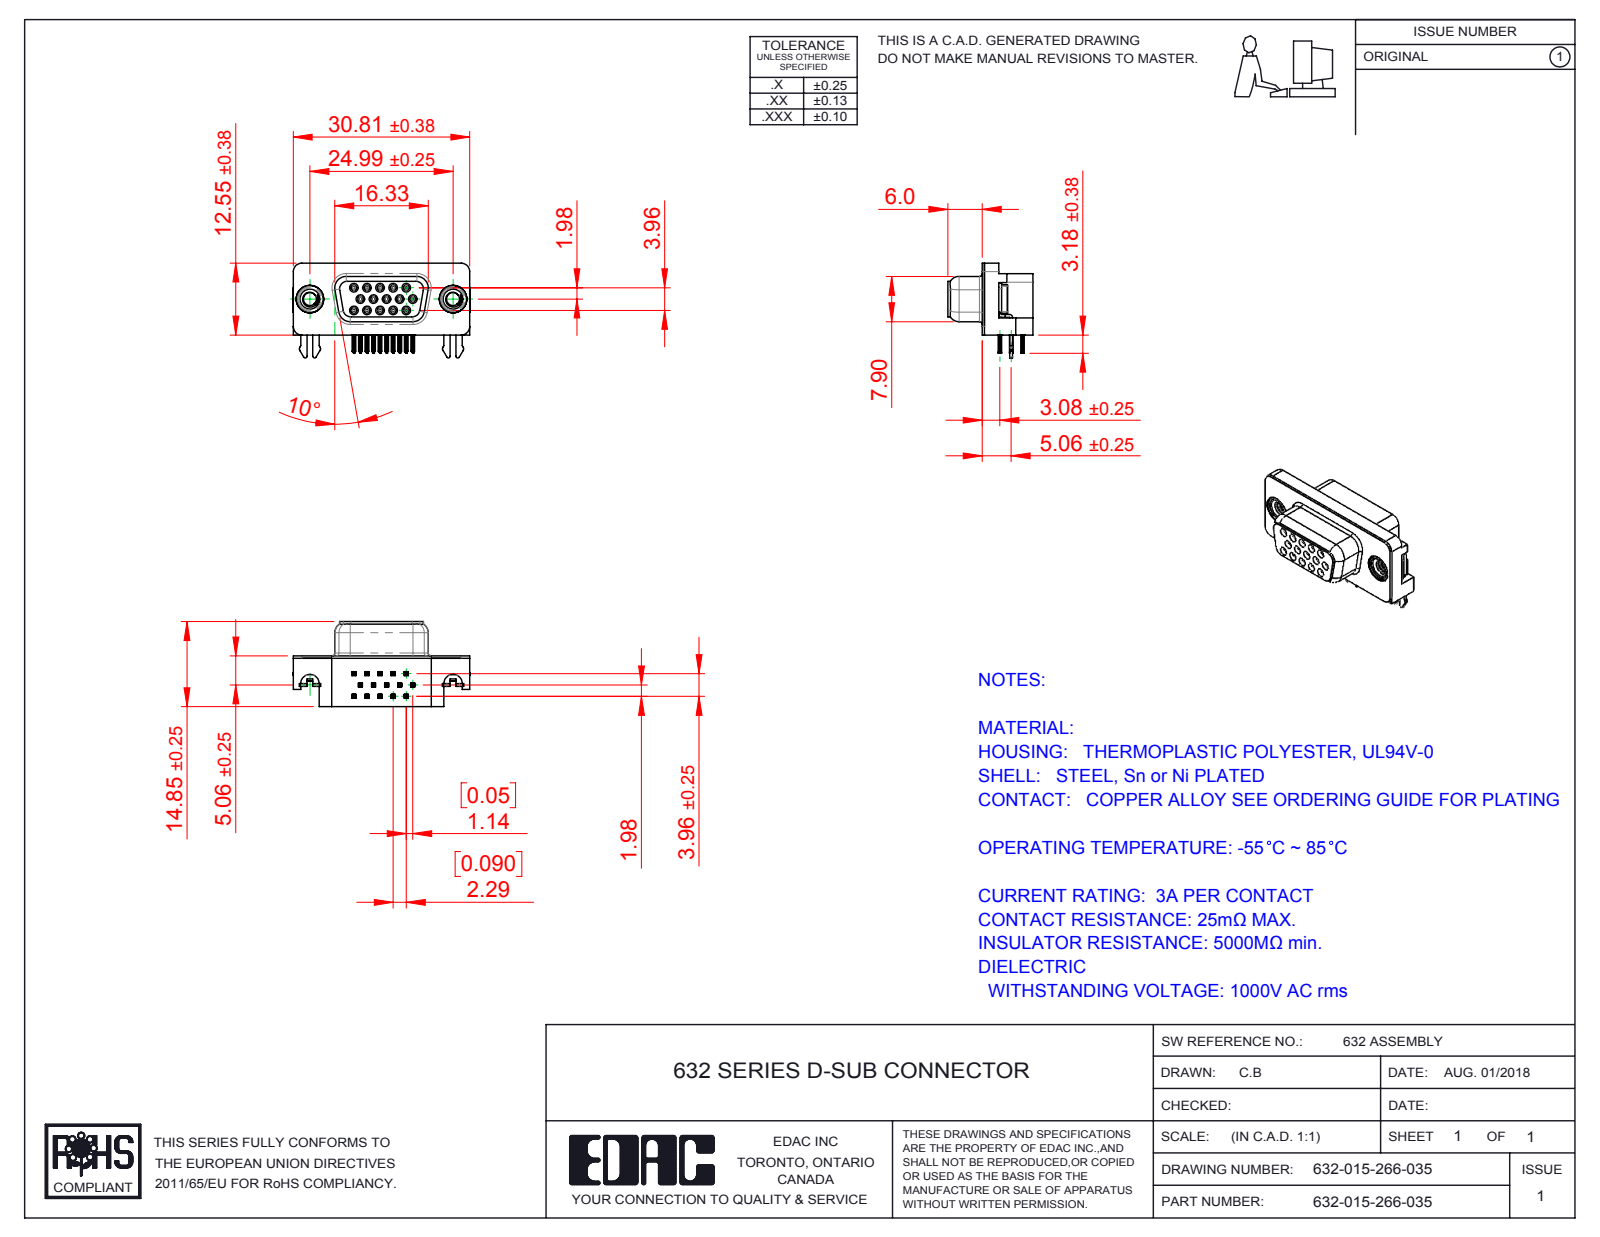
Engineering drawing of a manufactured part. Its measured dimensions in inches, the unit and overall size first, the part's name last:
Units: inches
Overall size (bounding box): 1.216 × 0.652 × 0.585
Round holes (diameter × count): ⌀0.031 ×15, ⌀0.035 ×15, ⌀0.089 ×2, ⌀0.098 ×2, ⌀0.157 ×2, ⌀0.189 ×2, ⌀0.197 ×2
Round bosses / shafts (diameter × count): ⌀0.047 ×15, ⌀0.193 ×2, ⌀0.187 ×2, ⌀0.154 ×2
Partial cylindrical surfaces — rounded edges, fillets, slot ends (radius × count): R0.004 ×120, R0.006 ×60, R0.014 ×30, R0.013 ×15, R0.039 ×11, R0.011 ×10, R0.02 ×10, R0.01 ×8
Main face-to-face distances: 0.016, 0.333, 0.348, 0.078, 0.114, 0.234, 0.098, 0.252, 0.264, 0.278
Hole centre spacings: 0.09, 0.09, 0.156, 0.18, 0.238, 0.156, 0.18, 0.27
Volume: 0.183 in³ · Surface area: 8.28 in²
Bodies: 23 solids, 2426 faces (1006 planar, 654 cylindrical, 766 other)
Part name (STEP PRODUCT): 632 4-40 Threaded Rivet; 632 2 Prong Board Lock; 632 Contact Top; 632 Contact Middle (+5 more)
STEP written by: SolidWorks 2016 (CONFIG_CONTROL_DESIGN)
